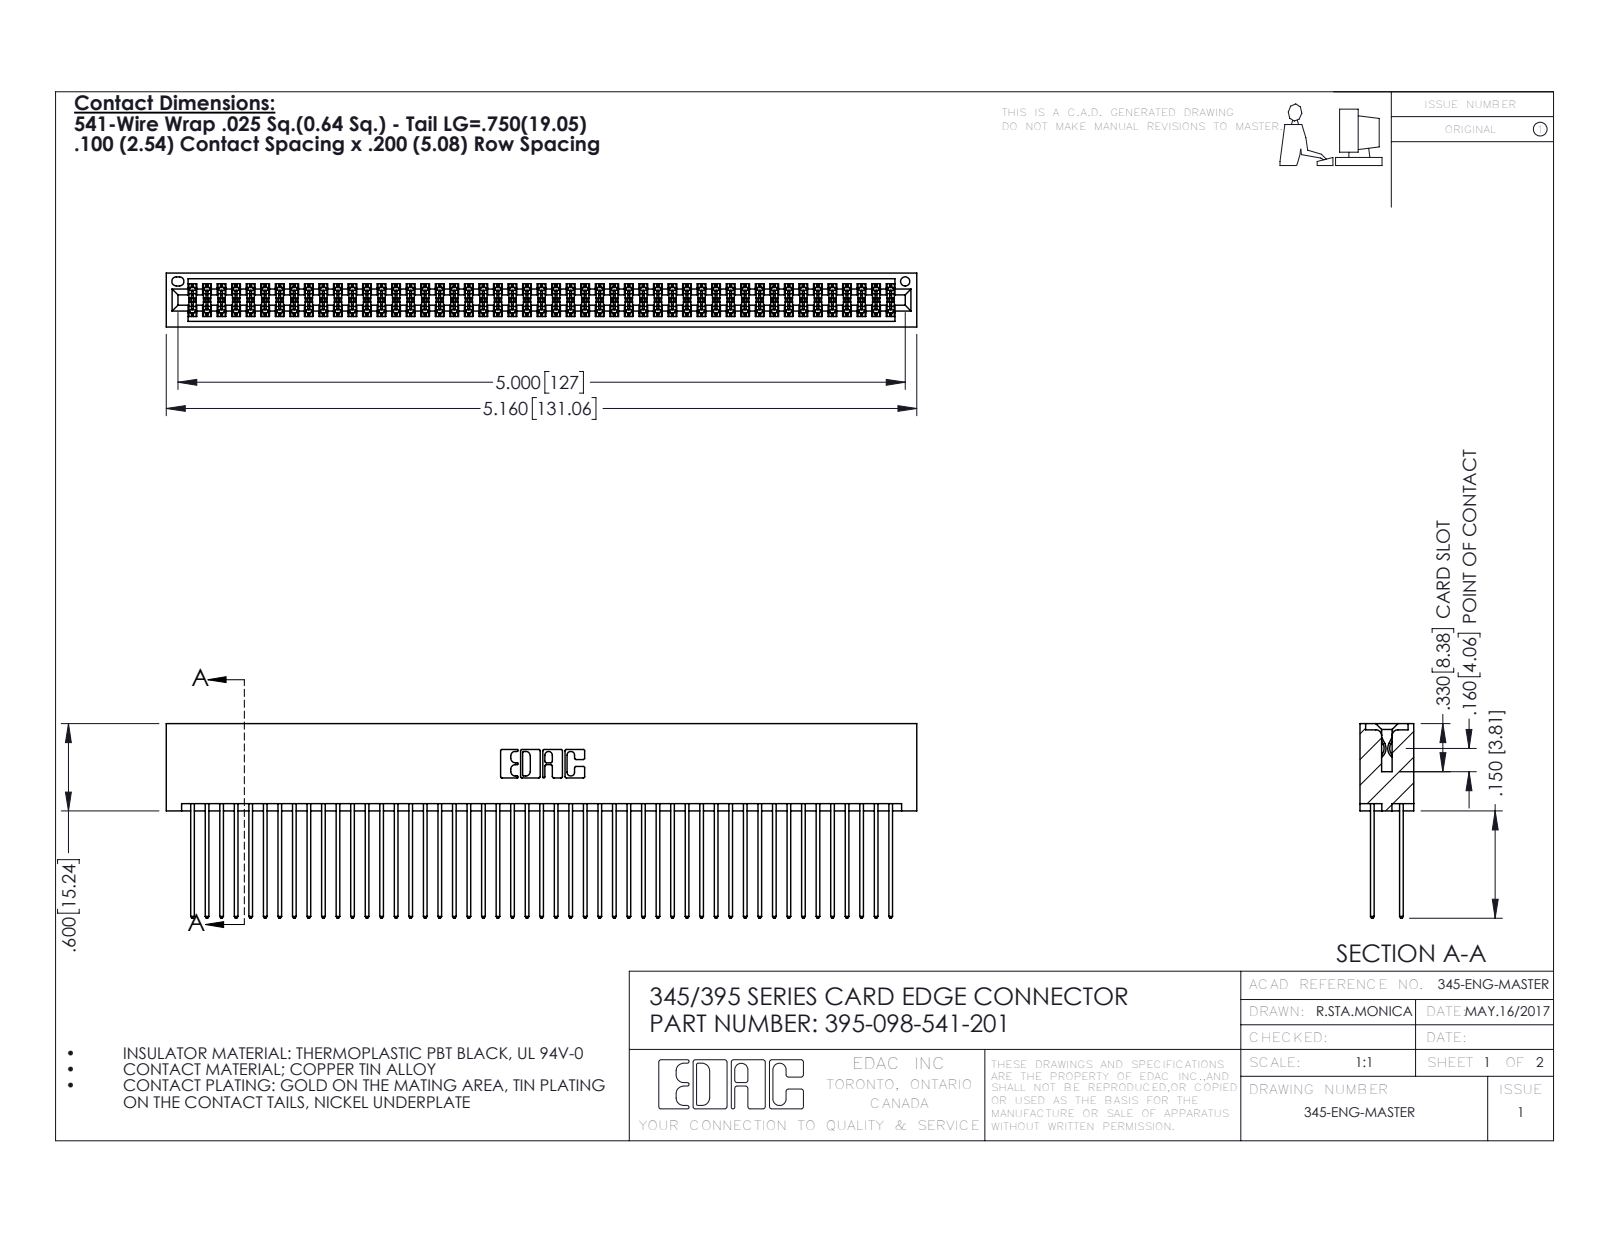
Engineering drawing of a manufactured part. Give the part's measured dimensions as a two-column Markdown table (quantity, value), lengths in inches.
| quantity | value |
| --- | --- |
| part name | 345-292-001_345-293-141; 345 Part_No Mounting Lugs; 395-098-541-201 |
| STEP written by | SolidWorks 2016 (CONFIG_CONTROL_DESIGN) |
| units | inches |
| bodies | 99 solids, 5018 faces (3310 planar, 1708 cylindrical, 0 other) |
| overall size | 5.16 × 1.337 × 0.37 |
| volume | 0.853 in³ |
| surface area | 36.8 in² |
| round holes (diameter × count) | 0.064 × 1 |
| partial cylindrical surfaces (radius × count) | 0.006 × 147, 0.01 × 98, 0.01 × 22, 0.007 × 6, 0.031 × 6, 0.026 × 3, 0.014 × 2, 0.019 × 2 |
| main face-to-face distances | 0.298, 0.072, 0.2, 0.098, 0.272, 0.025, 0.225, 0.37, 0.175, 0.149 |
